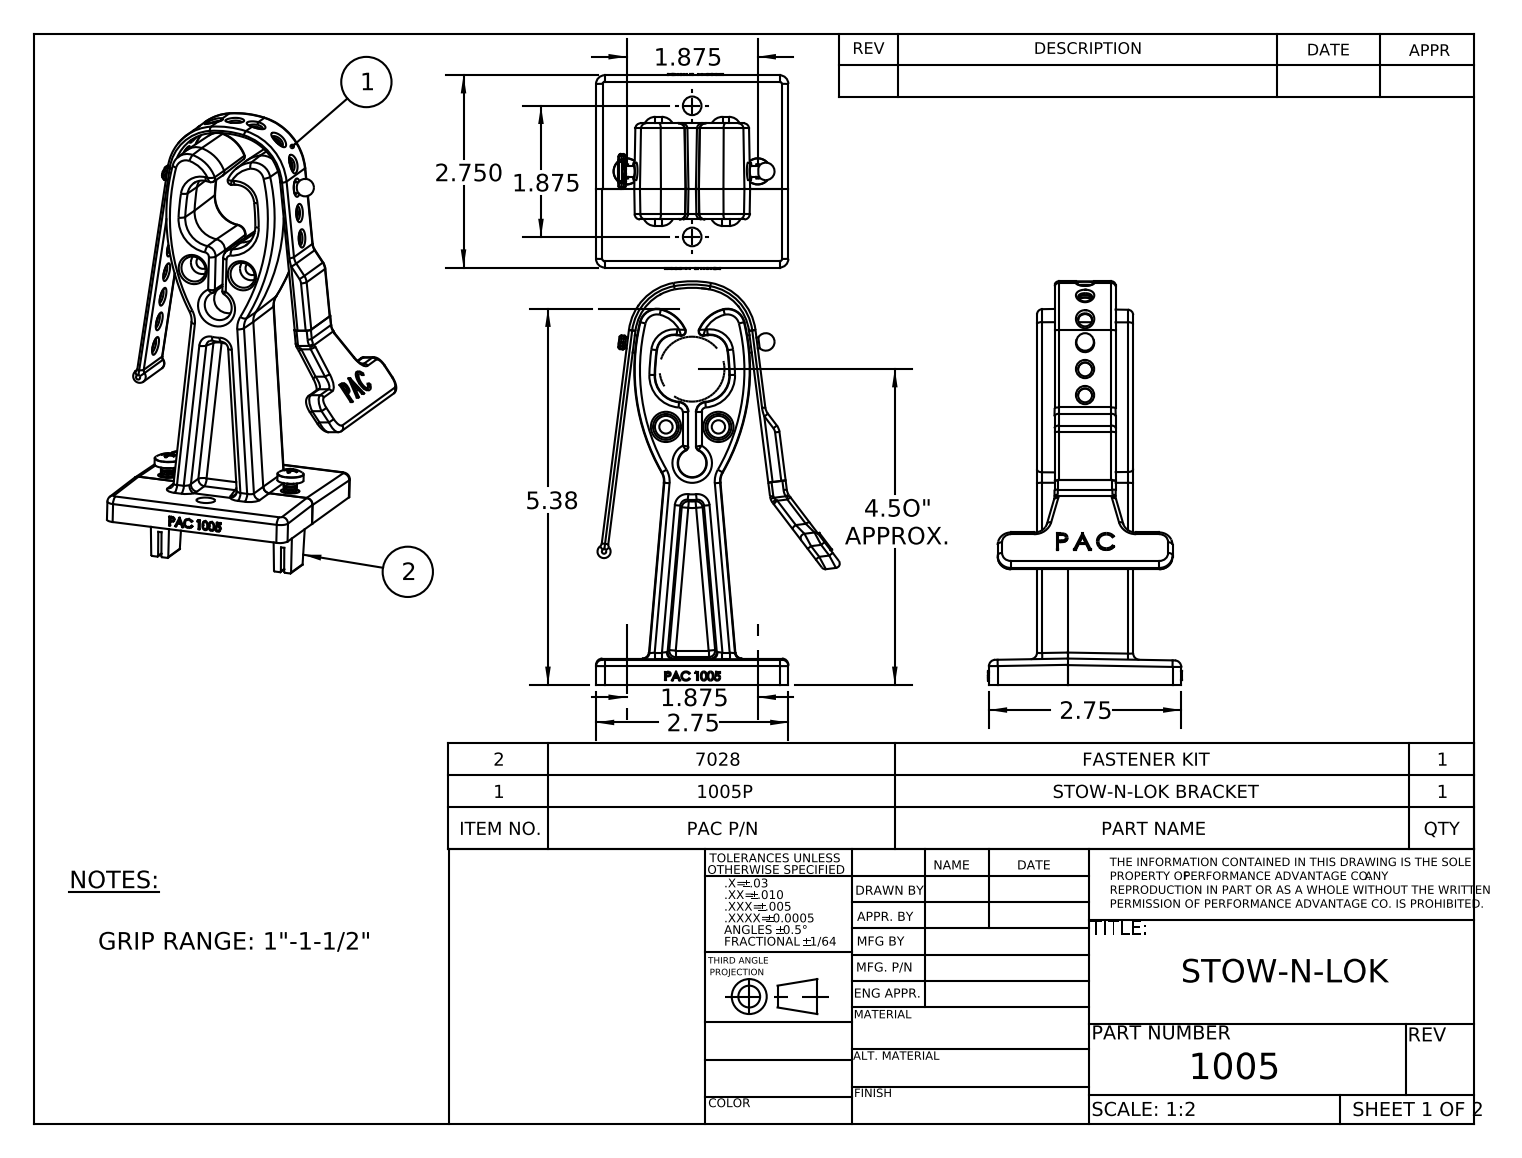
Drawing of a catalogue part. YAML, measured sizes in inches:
part_name: "2046; 2059_#10; 7016; 7028 (+3 more)"
step_written_by: "SolidWorks 2010 (CONFIG_CONTROL_DESIGN)"
units: inches
bodies: {solids: 30, faces: 1312, planar: 375, cylindrical: 256, other: 681}
overall_size: [6.552, 3.485, 2.781]
volume: 8.67
surface_area: 102.8
round_holes:
  - {diameter: 0.2, count: 18}
  - {diameter: 0.266, count: 4}
  - {diameter: 0.19, count: 2}
  - {diameter: 0.201, count: 2}
  - {diameter: 0.25, count: 2}
  - {diameter: 0.499, count: 2}
round_bosses_or_shafts:
  - {diameter: 0.5, count: 2}
  - {diameter: 0.375, count: 2}
  - {diameter: 0.187, count: 2}
  - {diameter: 0.156, count: 2}
partial_cylinders:
  - {radius: 0.031, count: 22}
  - {radius: 0.094, count: 20}
  - {radius: 0.062, count: 18}
  - {radius: 0.063, count: 16}
  - {radius: 0.075, count: 12}
  - {radius: 0.1, count: 10}
  - {radius: 0.187, count: 9}
  - {radius: 0.015, count: 8}
face_to_face_distances: [0.25, 0.188, 0.094, 0.687, 1.375, 0.437, 0.937, 2.062, 2.75, 0.192]
hole_center_spacings: [0.375, 0.75, 1.125, 1.326, 1.5, 1.875, 0.939, 1.875]
